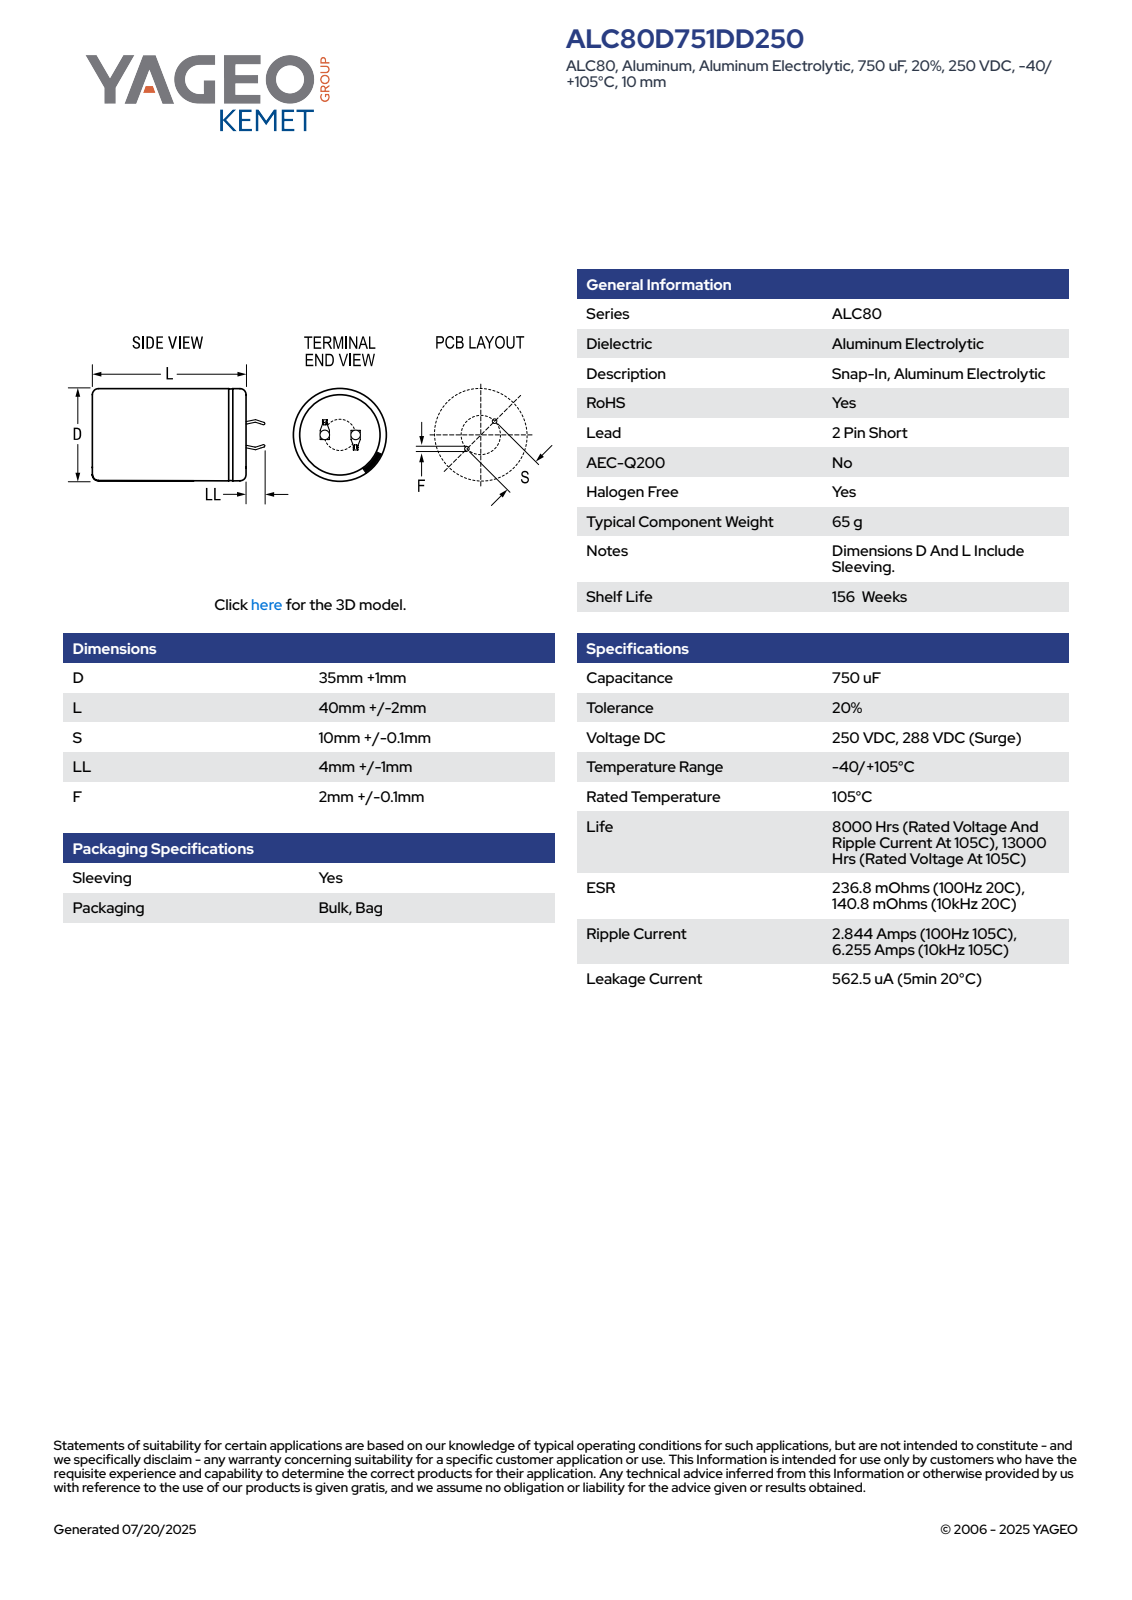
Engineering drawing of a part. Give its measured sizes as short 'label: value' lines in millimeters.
name: CARS_K2P_35X40_D36L42S10LL5F2.1
written by: SolidWorks 2014 (AUTOMOTIVE_DESIGN)
unit: mm
bodies: 1 solid, 100 faces (52 planar, 9 cylindrical, 39 other)
size: 46.99 × 36 × 36
volume: 42 221 mm³; area: 6 772 mm²
holes: 1× ⌀31.85
bosses: 1× ⌀36
rounds: 1× R17.99
face distances: 41.99, 42.49, 0.5, 7.08, 0.6, 0.59, 7.6, 0.75, 1.35, 7.68
